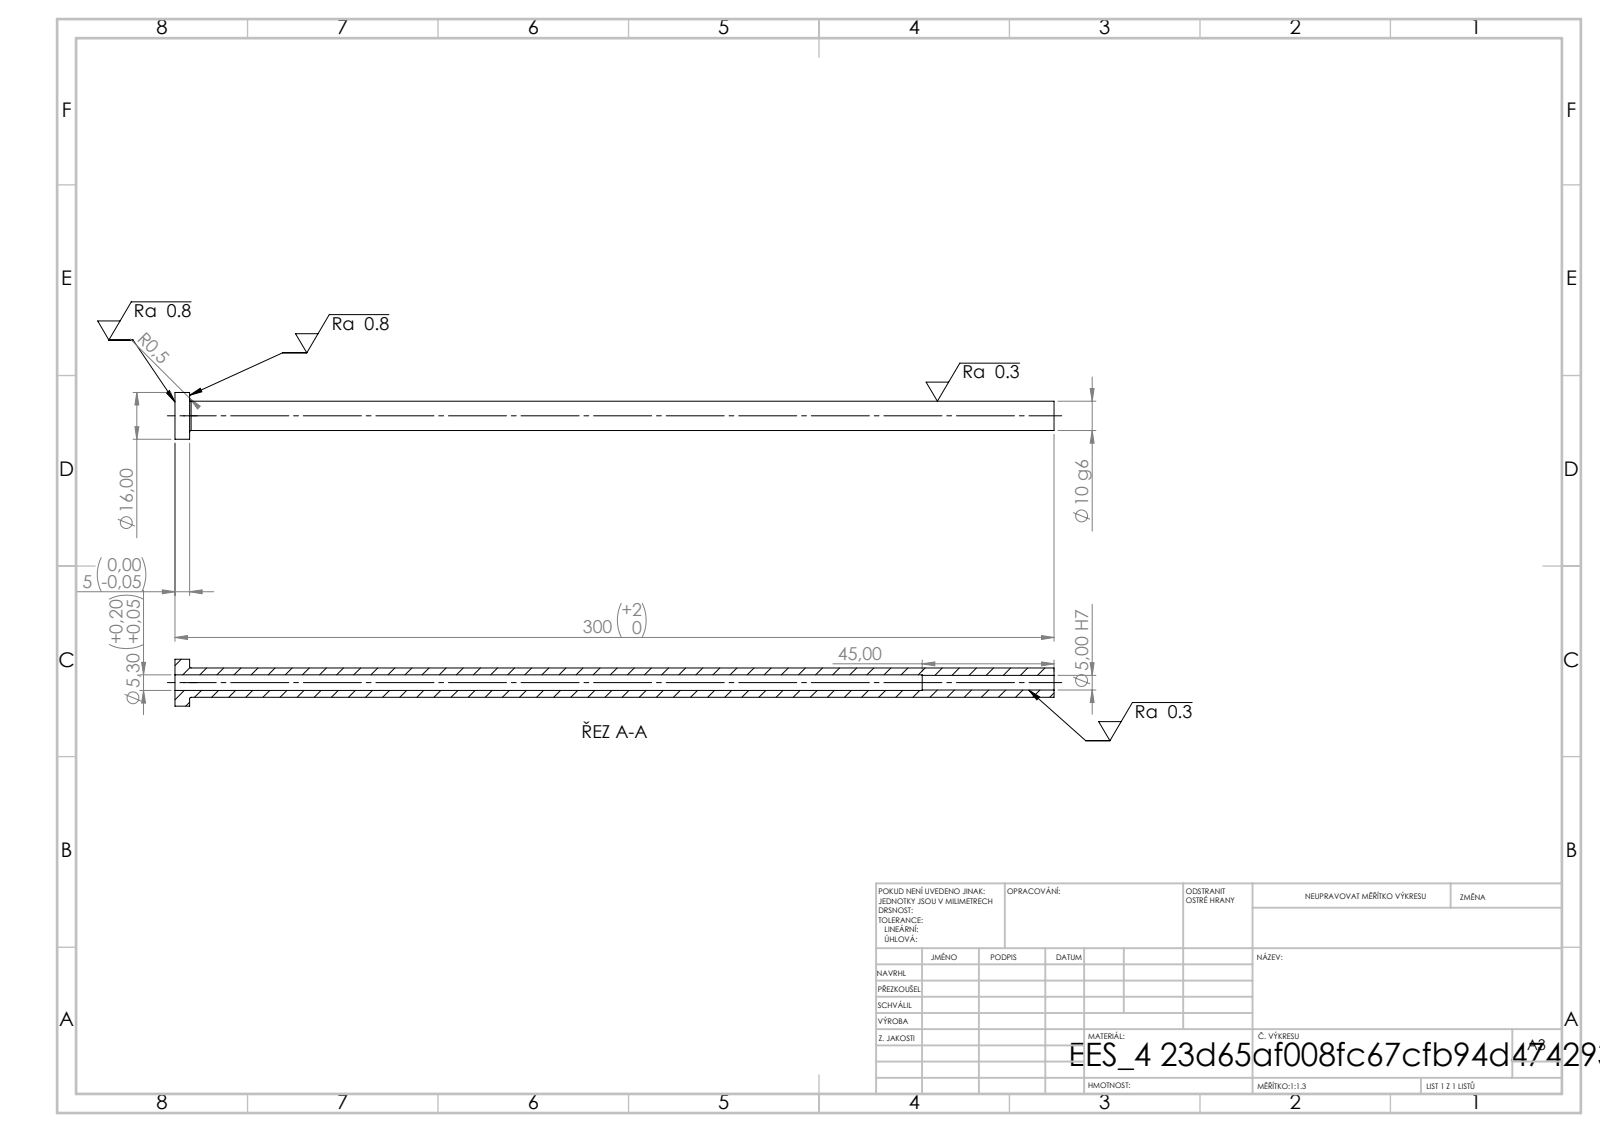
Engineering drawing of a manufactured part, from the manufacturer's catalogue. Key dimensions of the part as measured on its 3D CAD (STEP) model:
STEP written by: SolidWorks 2019 (CONFIG_CONTROL_DESIGN)
Units: millimetres
Bodies: 1 solid, 14 faces (4 planar, 8 cylindrical, 2 other)
Overall size (bounding box): 300 × 16 × 16
Volume: 17 667 mm³ · Surface area: 14 828 mm²
Round holes (diameter × count): ⌀5 ×1, ⌀5.3 ×1
Round bosses / shafts (diameter × count): ⌀16 ×1, ⌀10 ×1
Main face-to-face distances: 5, 300, 295, 255, 250, 45
